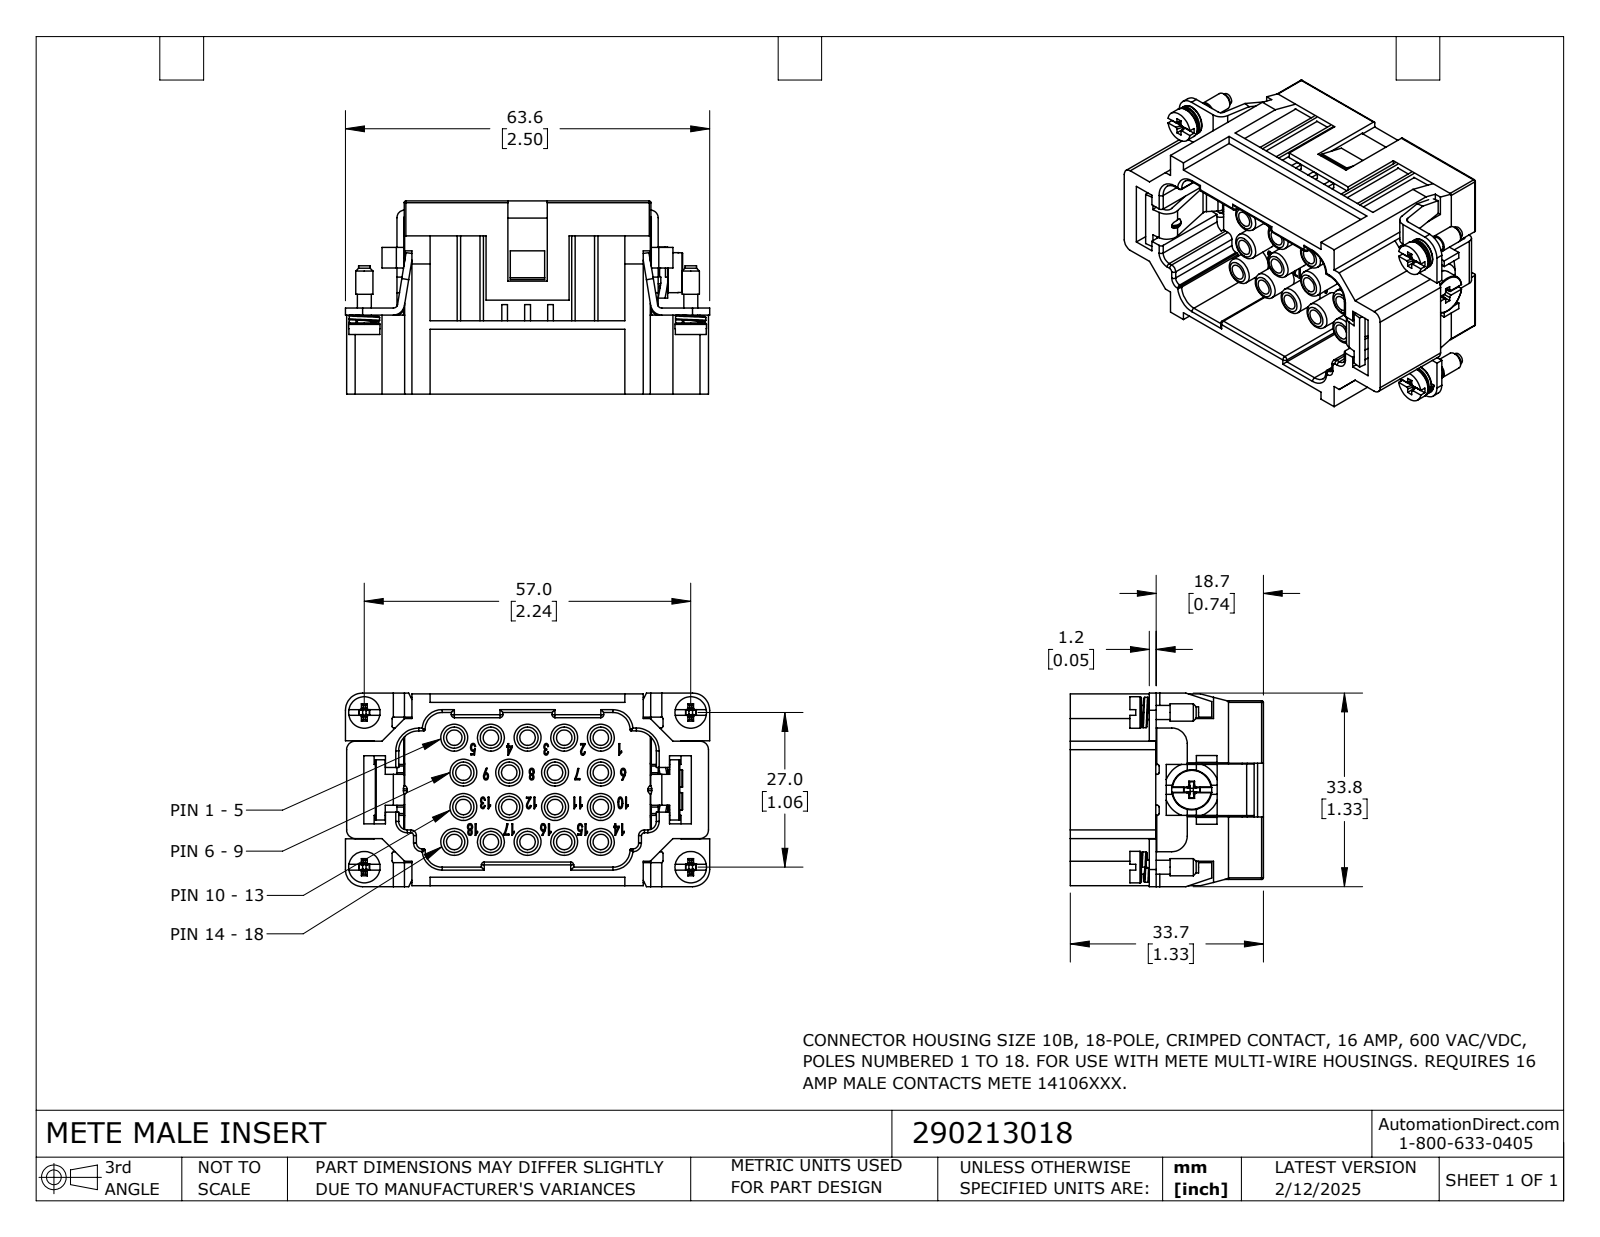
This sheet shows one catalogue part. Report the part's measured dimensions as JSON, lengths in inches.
{"part_name": "290213018", "step_written_by": "SolidWorks 2024 (CONFIG_CONTROL_DESIGN)", "units": "inches", "bodies": {"solids": 14, "faces": 2073, "planar": 1131, "cylindrical": 549, "other": 393}, "overall_size": [2.504, 1.331, 1.327], "volume_in3": 1.618, "surface_area_in2": 48.34, "round_holes": [[0.106, 18], [0.189, 18], [0.067, 8], [0.114, 4], [0.11, 3], [0.13, 1]], "round_bosses_or_shafts": [[0.185, 18], [0.063, 8], [0.217, 4], [0.209, 4], [0.118, 4], [0.096, 4], [0.079, 4], [0.106, 3]], "partial_cylinders_radius": [[0.165, 36], [0.01, 32], [0.02, 31], [0.118, 26], [0.059, 24], [0.012, 20], [0.096, 18], [0.004, 10]], "face_to_face_distances": [0.047, 0.118, 0.049, 0.024, 0.642, 0.228, 0.163, 0.76, 0.035, 0.033], "hole_center_spacings": [0.637, 0.156, 0.252, 0.315, 0.759, 0.887, 0.17, 0.226]}
